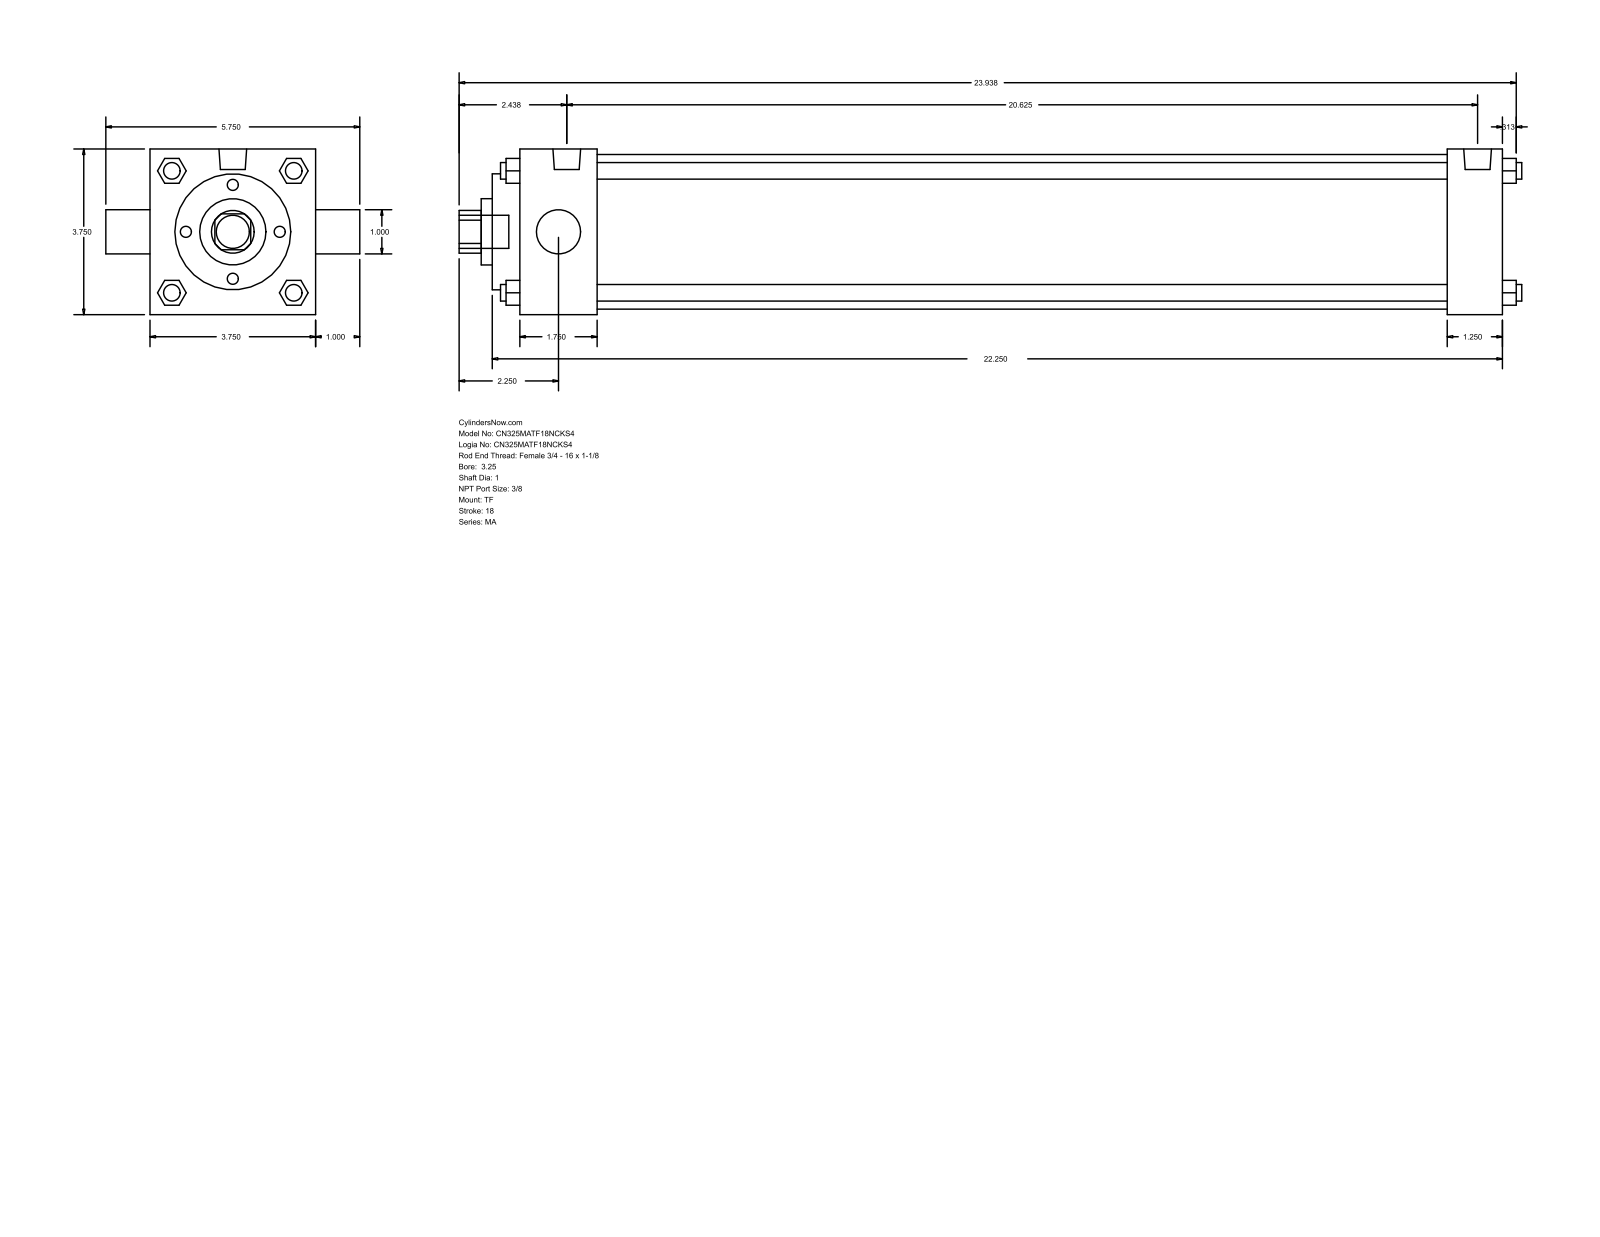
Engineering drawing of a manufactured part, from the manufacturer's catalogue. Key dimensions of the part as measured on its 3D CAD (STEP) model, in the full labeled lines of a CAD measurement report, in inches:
Part name (STEP PRODUCT): MA_TF__0325_1
STEP written by: GSSL Pune (CONFIG_CONTROL_DESIGN)
Units: inches
Bodies: 0 solids, 122 faces (93 planar, 29 cylindrical, 0 other)
Overall size (bounding box): 24.063 × 5.75 × 3.75
Round holes (diameter × count): ⌀1 ×2, ⌀1.5 ×1, ⌀2.625 ×1, ⌀3.5 ×1
Round bosses / shafts (diameter × count): ⌀0.375 ×4, ⌀0.437 ×3, ⌀0.627 ×2, ⌀0.75 ×1
Partial cylindrical surfaces — rounded edges, fillets, slot ends (radius × count): R0.484 ×1
Main face-to-face distances: 3.75, 22.25, 0.625, 1.75, 21, 19.25, 20.5, 1.25, 2.375, 21.625
